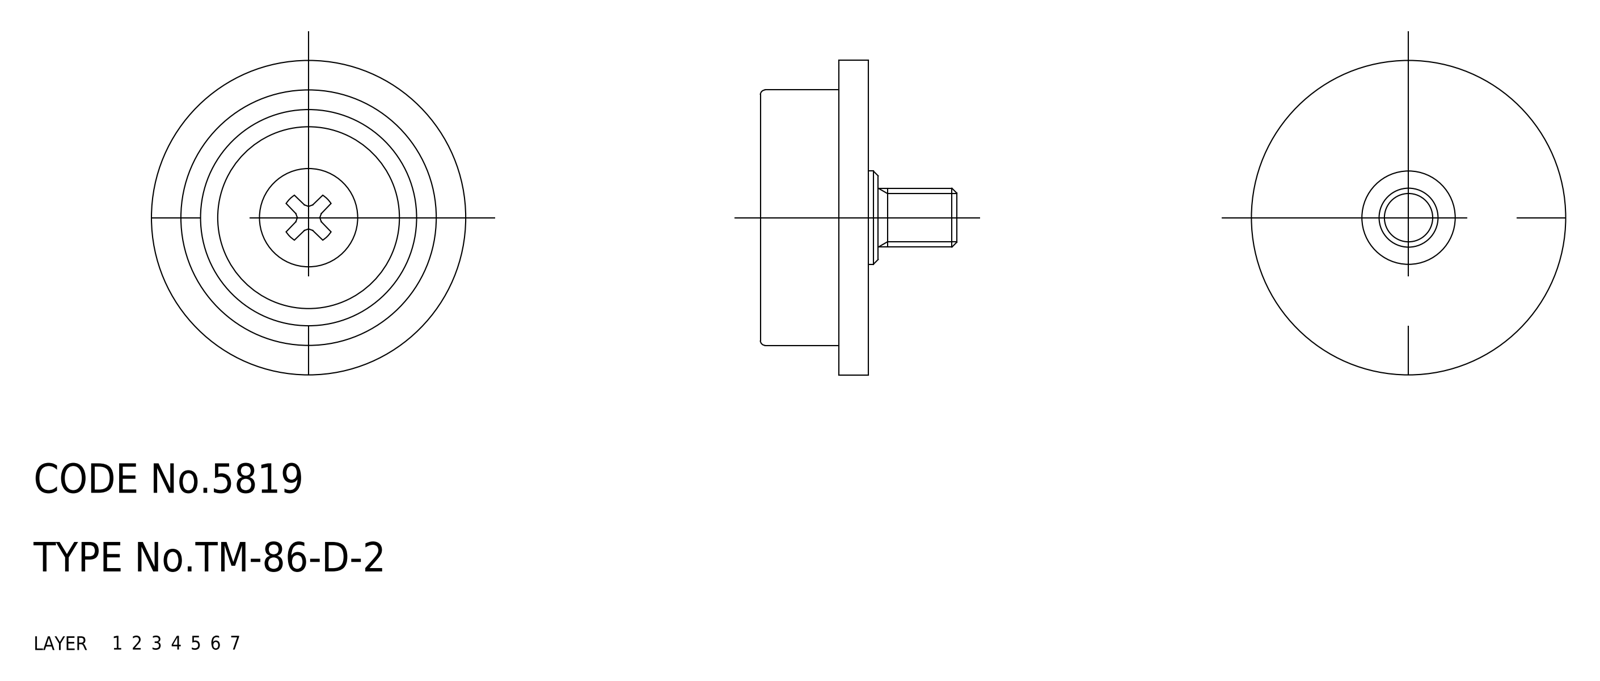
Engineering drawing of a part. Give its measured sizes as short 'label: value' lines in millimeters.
name: roller
written by: CADfix (AUTOMOTIVE_DESIGN)
unit: mm
bodies: 1 solid, 57 faces (0 planar, 0 cylindrical, 57 other)
size: 32 × 32 × 20
volume: 5 827 mm³; area: 3 653 mm²
